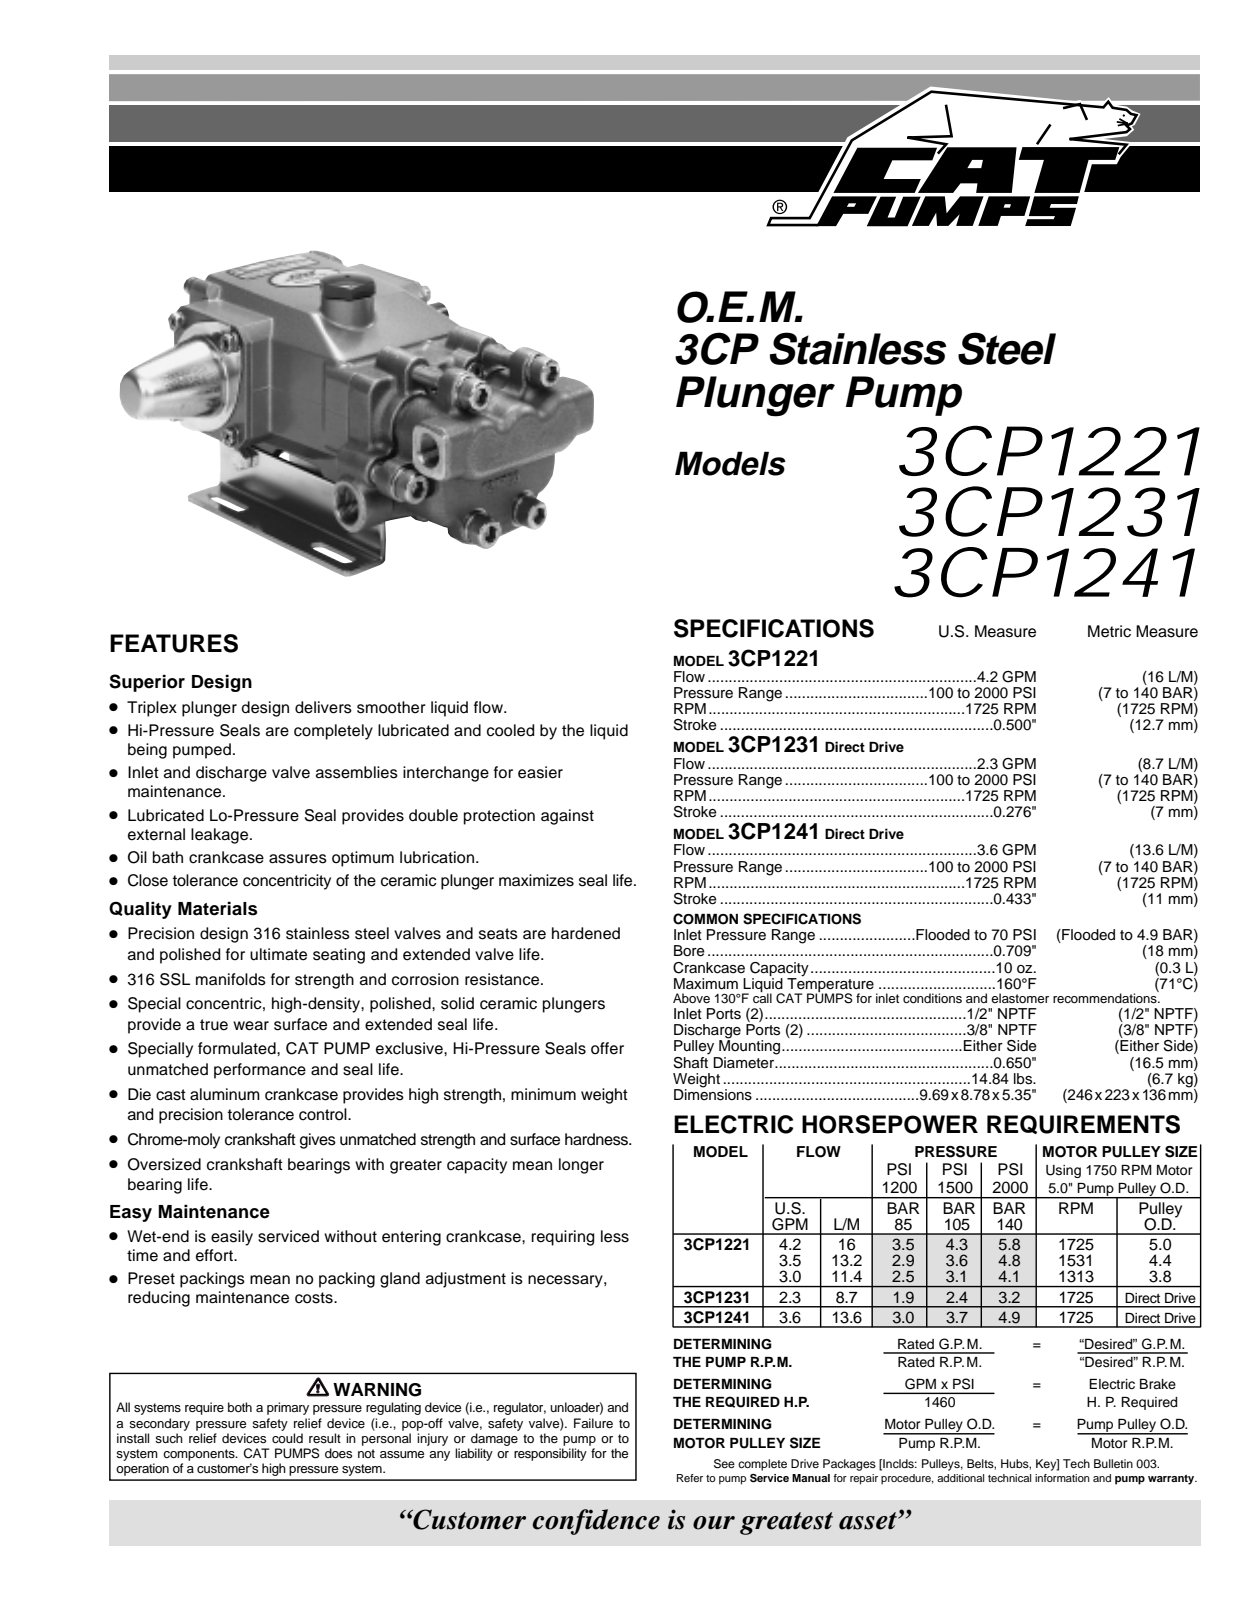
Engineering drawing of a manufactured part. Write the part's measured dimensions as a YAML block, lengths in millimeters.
part_name: "3CP 1221"
step_written_by: "SolidWorks 2016 (AUTOMOTIVE_DESIGN)"
units: millimeters
bodies: {solids: 0, faces: 2290, planar: 738, cylindrical: 732, other: 820}
overall_size: [245, 223, 145.2]
round_holes:
  - {diameter: 8, count: 10}
  - {diameter: 11, count: 6}
  - {diameter: 6, count: 4}
  - {diameter: 7, count: 4}
  - {diameter: 9, count: 2}
  - {diameter: 12, count: 2}
  - {diameter: 14.1, count: 2}
  - {diameter: 20, count: 2}
  - {diameter: 2, count: 1}
  - {diameter: 5, count: 1}
  - {diameter: 14, count: 1}
  - {diameter: 14.5, count: 1}
round_bosses_or_shafts:
  - {diameter: 11, count: 8}
  - {diameter: 18.1, count: 6}
  - {diameter: 16, count: 6}
  - {diameter: 9.8, count: 6}
  - {diameter: 9.9, count: 4}
  - {diameter: 28.8, count: 3}
  - {diameter: 30, count: 2}
  - {diameter: 13, count: 2}
partial_cylinders:
  - {radius: 1, count: 114}
  - {radius: 0.5, count: 56}
  - {radius: 1.5, count: 40}
  - {radius: 2, count: 39}
  - {radius: 6, count: 20}
  - {radius: 3, count: 17}
  - {radius: 0.3, count: 16}
  - {radius: 2.5, count: 10}
face_to_face_distances: [4, 76, 19, 3, 44, 52, 72, 47, 13.5, 16]
hole_center_spacings: [38, 53.74, 59.99, 100, 14.53, 19.24, 23.05, 23.07]
